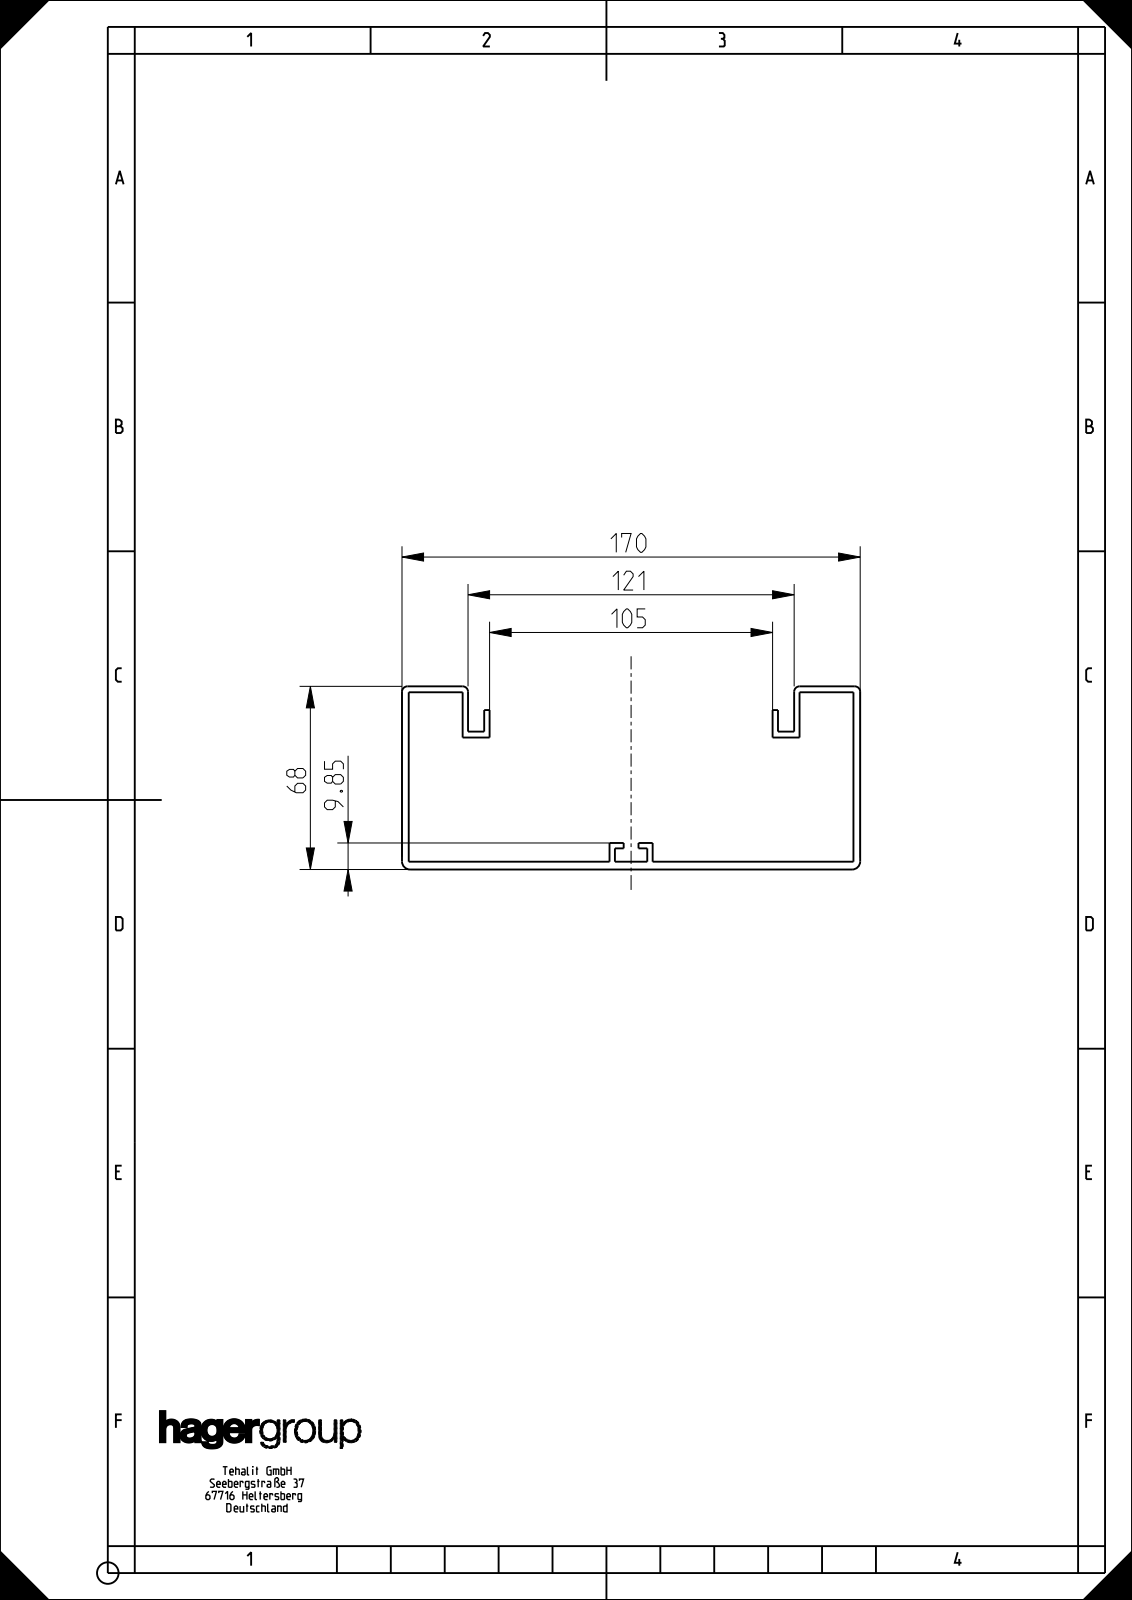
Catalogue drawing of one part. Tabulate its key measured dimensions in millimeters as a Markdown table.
| quantity | value |
| --- | --- |
| part name | BR651701B |
| STEP written by | CREO PARAMETRIC BY PTC INC, 2022024 (AUTOMOTIVE_DESIGN) |
| units | millimeters |
| bodies | 1 solid, 700 faces (534 planar, 166 cylindrical, 0 other) |
| overall size | 2000 × 170 × 68 |
| volume | 2 151 000 mm³ |
| surface area | 1 721 000 mm² |
| partial cylindrical surfaces (radius × count) | 2.3 × 80, 3.25 × 40, 2 × 4, 3 × 2 |
| main face-to-face distances | 2.9, 2.5, 167.5, 170, 165, 2, 2.2, 68, 65.1, 8 |
